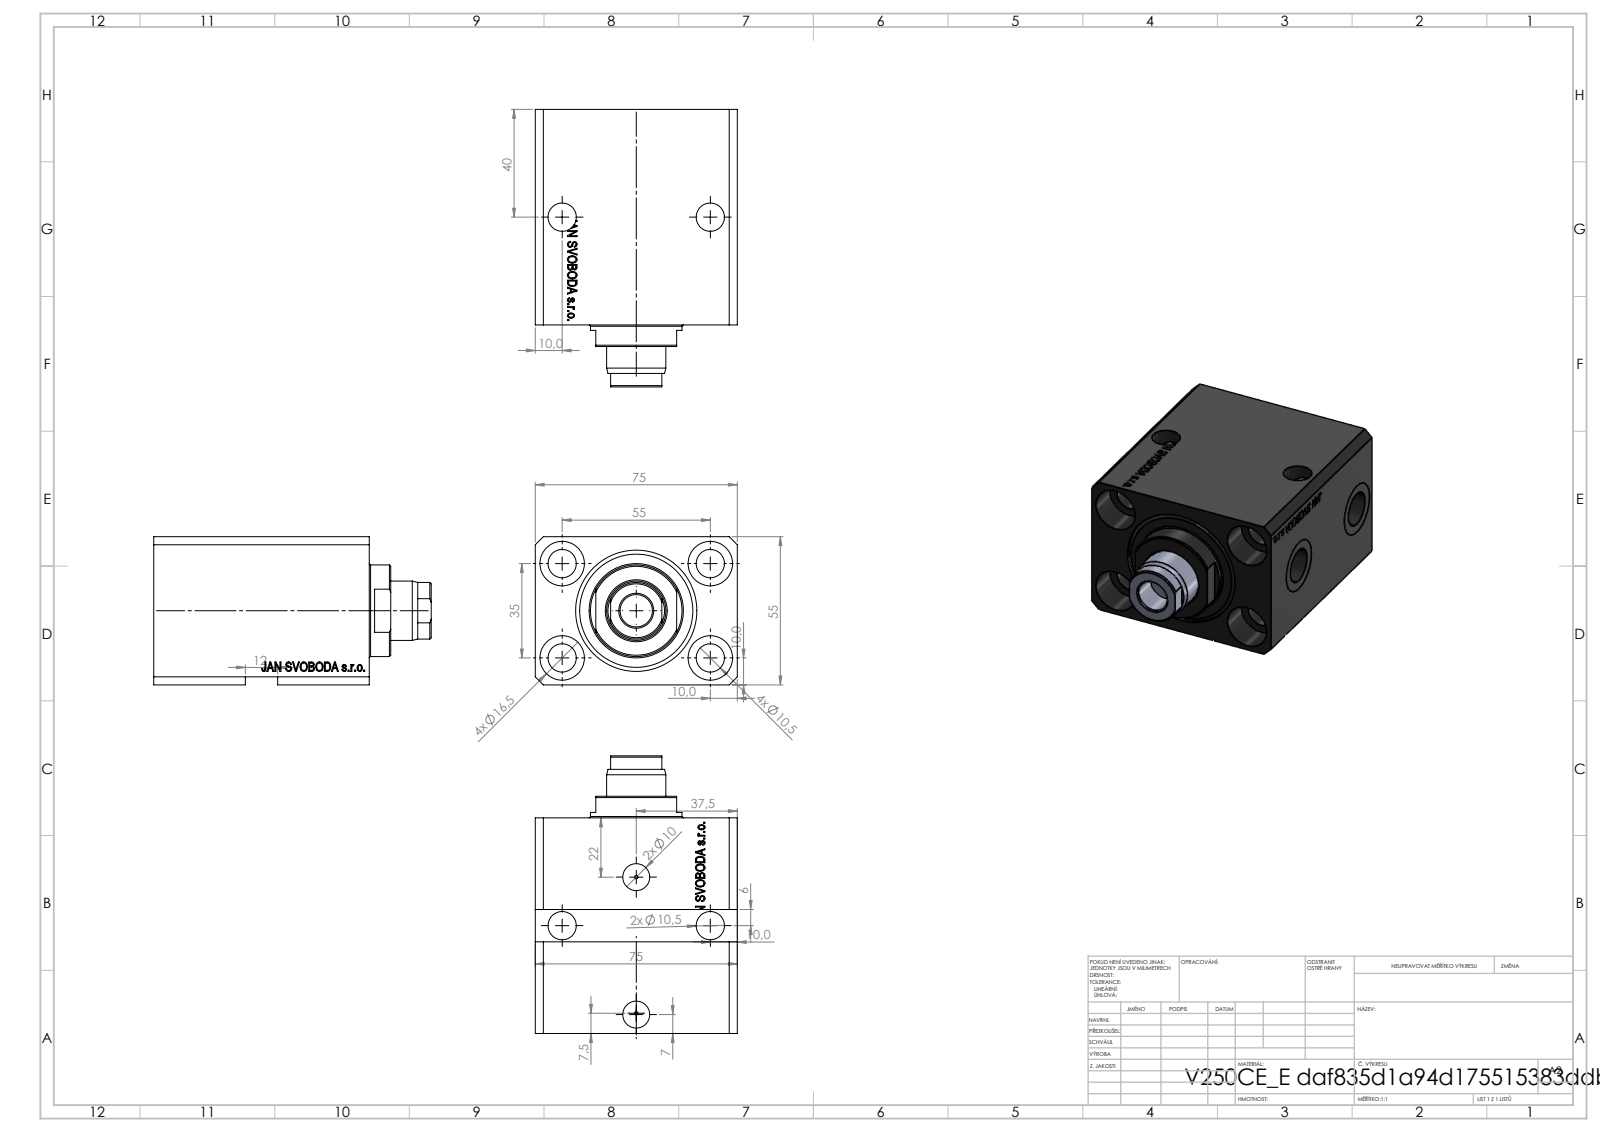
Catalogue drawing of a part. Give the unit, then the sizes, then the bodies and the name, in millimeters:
Units: millimetres
Overall size (bounding box): 103 × 75 × 55
Round holes (diameter × count): ⌀10.5 ×6, ⌀1.25 ×4, ⌀16.5 ×4, ⌀10 ×2, ⌀13.16 ×2, ⌀20 ×2, ⌀12 ×1, ⌀22 ×1, ⌀32 ×1, ⌀45 ×1
Round bosses / shafts (diameter × count): ⌀34 ×1
Partial cylindrical surfaces — rounded edges, fillets, slot ends (radius × count): R10.5 ×1
Main face-to-face distances: 55, 75, 12, 58, 80, 68, 10, 70, 69, 11
Hole centre spacings: 32.6, 55, 32.87, 35, 42.55, 42.96, 65.19, 0.53
Volume: 279 785 mm³ · Surface area: 66 629 mm²
Bodies: 3 solids, 885 faces (435 planar, 82 cylindrical, 368 other)
Part name (STEP PRODUCT): V250CE_C_VCP; V250CE_E; V250CE_E_vnitrni cast pro vysunuti
STEP written by: SolidWorks 2019 (CONFIG_CONTROL_DESIGN)
